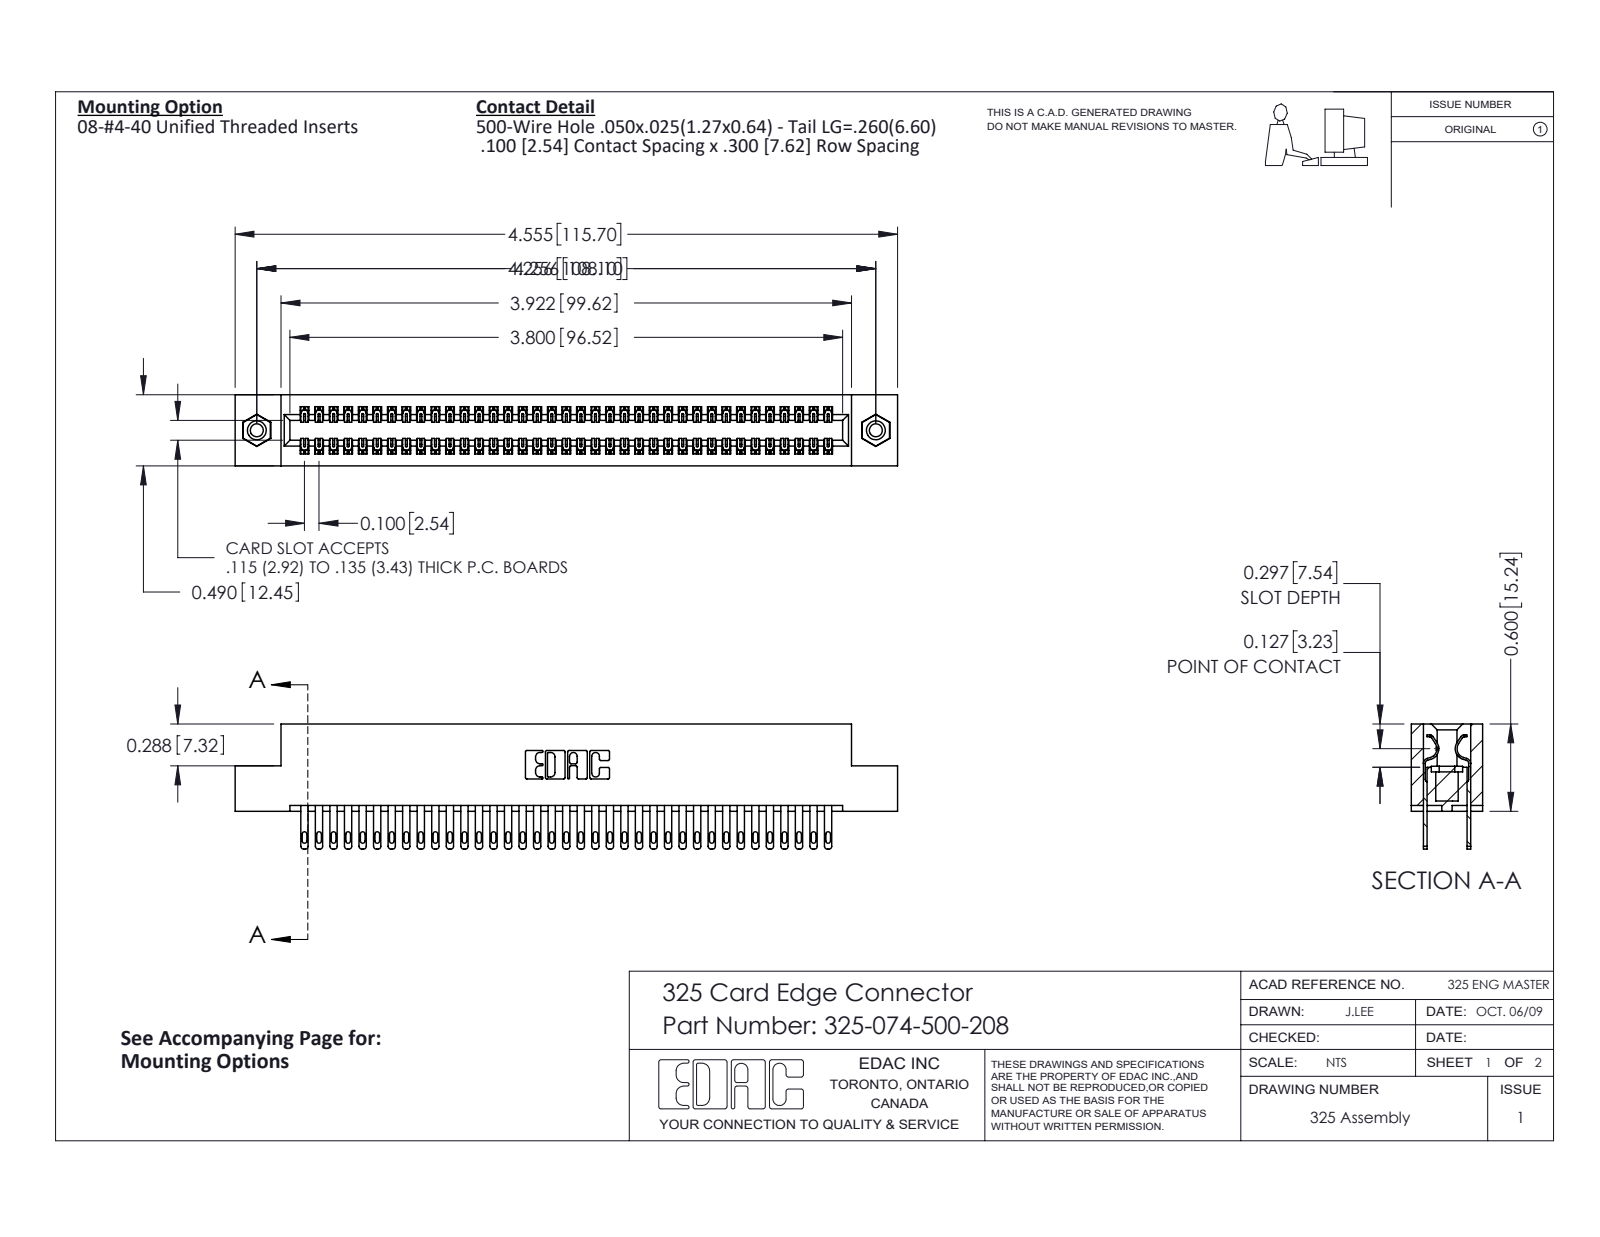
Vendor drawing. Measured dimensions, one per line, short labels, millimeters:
name: 325-292-001_325-293-100; 325-074-500-208; 345-250-001_345-250-003-102; 325 Part_TI
written by: SolidWorks 2016 (CONFIG_CONTROL_DESIGN)
unit: mm
bodies: 77 solids, 3726 faces (2322 planar, 1388 cylindrical, 16 other)
size: 115.7 × 21.8 × 12.4
volume: 15 100 mm³; area: 18 960 mm²
holes: 2× ⌀2.3, 2× ⌀3.2, 2× ⌀4.1
bosses: 2× ⌀3.9
rounds: 111× R0.2, 74× R0.4, 74× R0.5, 22× R0.3, 6× R0.2, 6× R0.8, 3× R0.7, 2× R0.4
face distances: 2.1, 10.3, 7.6, 2.7, 9.7, 0.6, 12.4, 8.3, 7, 14.2
hole spacings: 108.1
